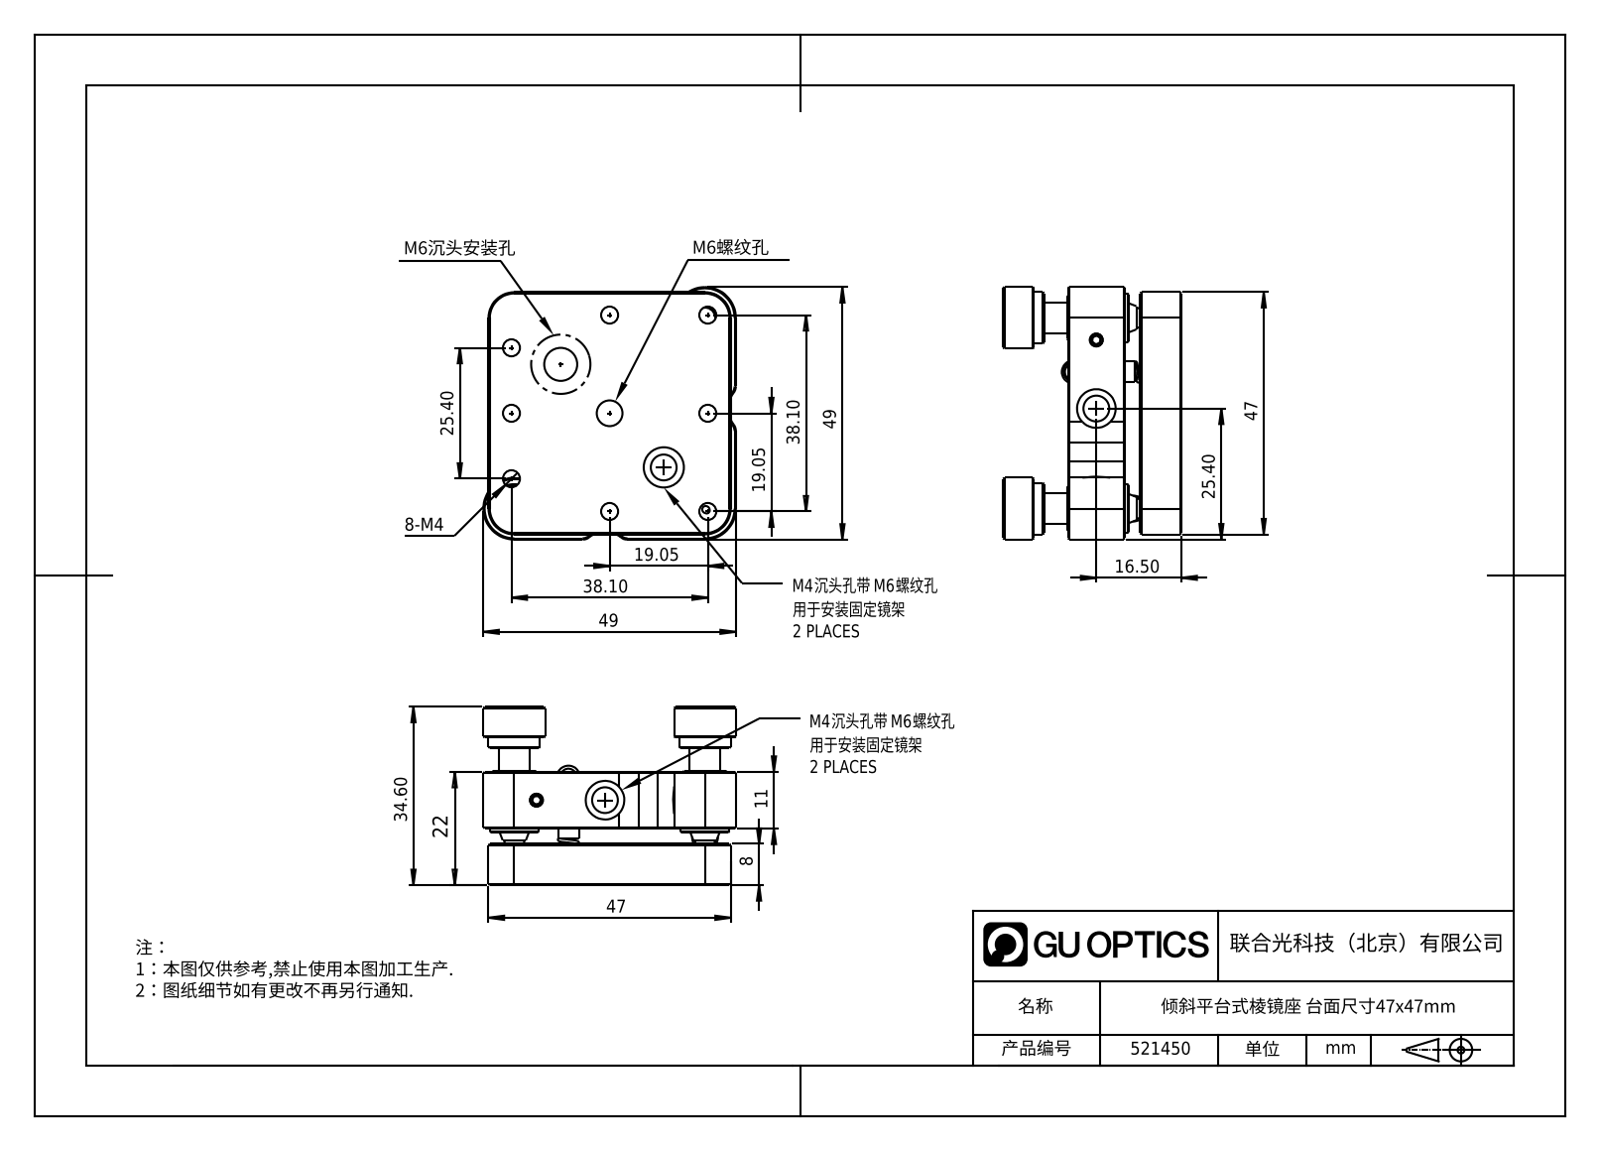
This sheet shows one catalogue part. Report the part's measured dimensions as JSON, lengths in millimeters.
{"part_name": "521450", "step_written_by": "SolidWorks 2020 (CONFIG_CONTROL_DESIGN)", "units": "millimeters", "bodies": {"solids": 0, "faces": 237, "planar": 98, "cylindrical": 64, "other": 75}, "overall_size": [49, 49, 34.1], "round_holes": [[5, 3], [8.6, 3], [9.5, 3], [4, 2], [6, 2], [7.5, 2], [10, 2], [2.5, 1]], "round_bosses_or_shafts": [[3.3, 8], [12, 2], [6, 2], [4, 2], [1.5, 2], [11.5, 1], [7.8, 1], [6.4, 1]], "partial_cylinders_radius": [[5, 5], [0.8, 4], [2, 4], [0.78, 2], [4, 2], [6, 1]], "face_to_face_distances": [8, 11, 3, 14, 22, 1, 48, 47, 12, 36], "hole_center_spacings": [10.5, 20.16, 26.5, 30.08, 37, 45.51, 11.31, 14.5]}
